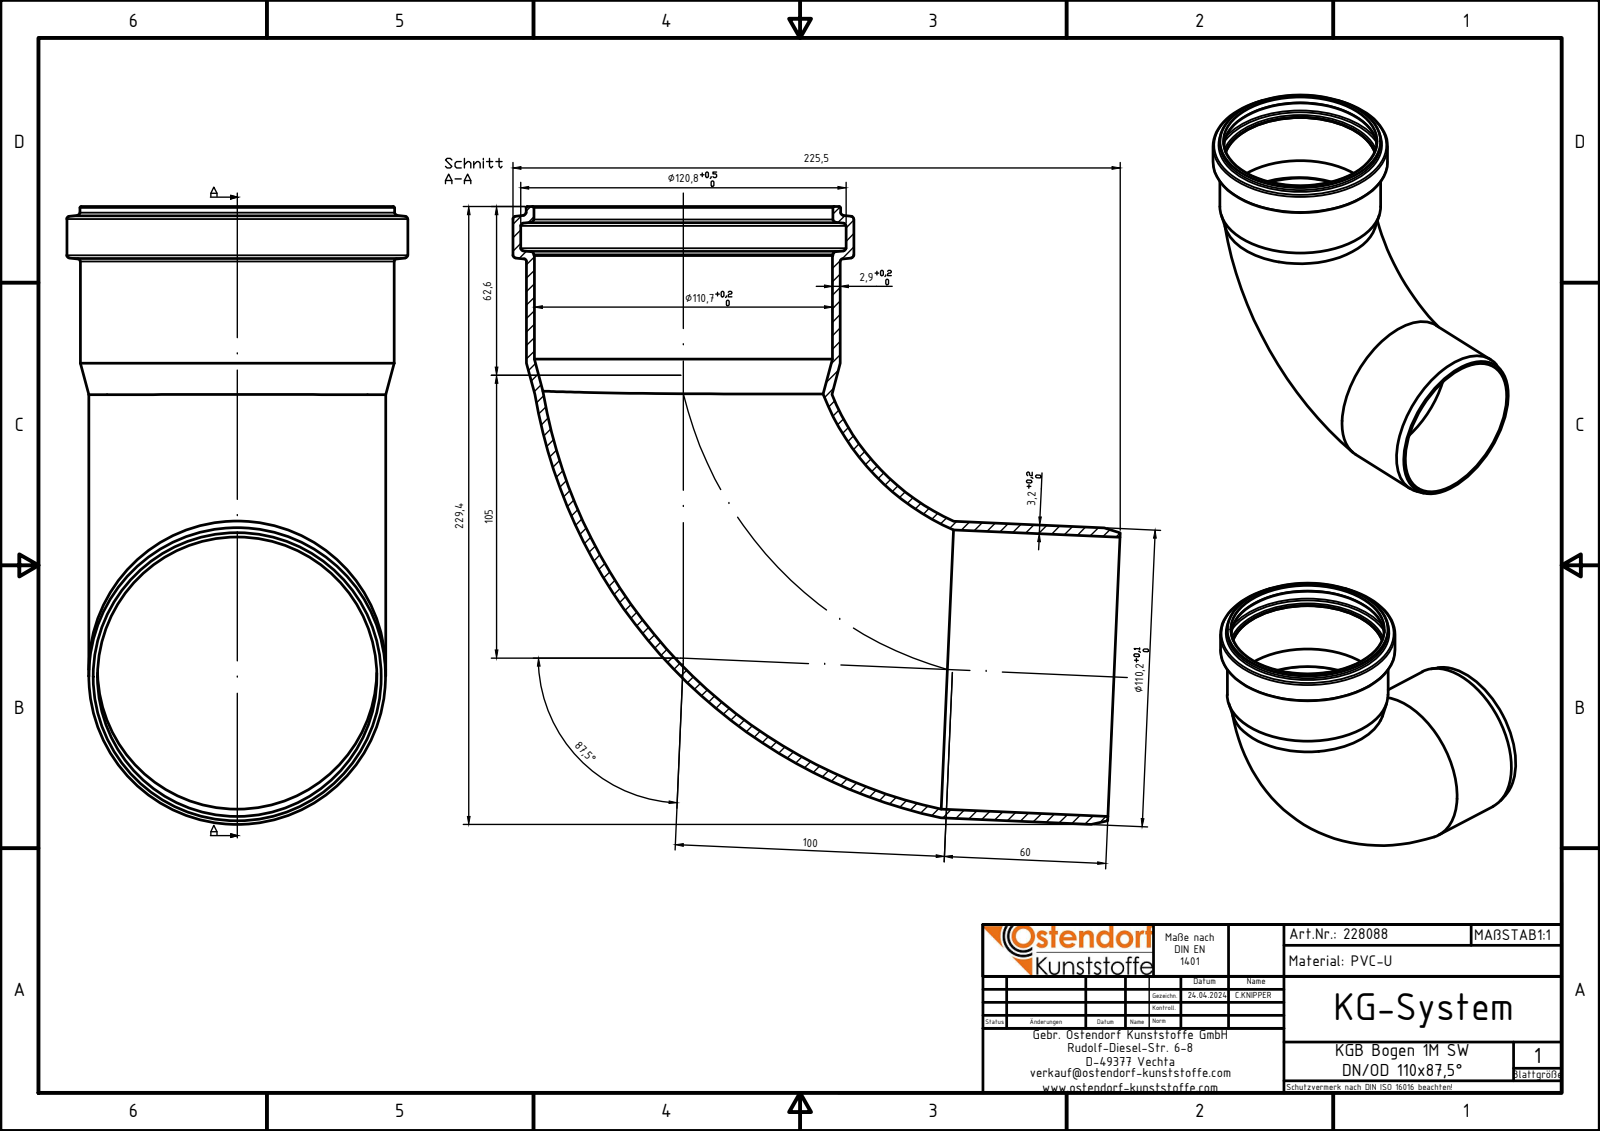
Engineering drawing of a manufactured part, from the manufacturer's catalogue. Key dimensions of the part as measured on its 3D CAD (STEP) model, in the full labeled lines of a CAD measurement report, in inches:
Part name (STEP PRODUCT): 228088
STEP written by: Autodesk Inventor 2024 (AUTOMOTIVE_DESIGN)
Units: inches
Bodies: 1 solid, 34 faces (5 planar, 9 cylindrical, 20 other)
Overall size (bounding box): 9.03 × 8.877 × 4.984
Volume: 18.61 in³ · Surface area: 307.2 in²
Round holes (diameter × count): ⌀4.087 ×1, ⌀4.358 ×1, ⌀4.37 ×1, ⌀4.756 ×1
Round bosses / shafts (diameter × count): ⌀4.984 ×1, ⌀4.598 ×1, ⌀4.587 ×1, ⌀4.339 ×1
Main face-to-face distances: 0.717, 2.033, 2.75
